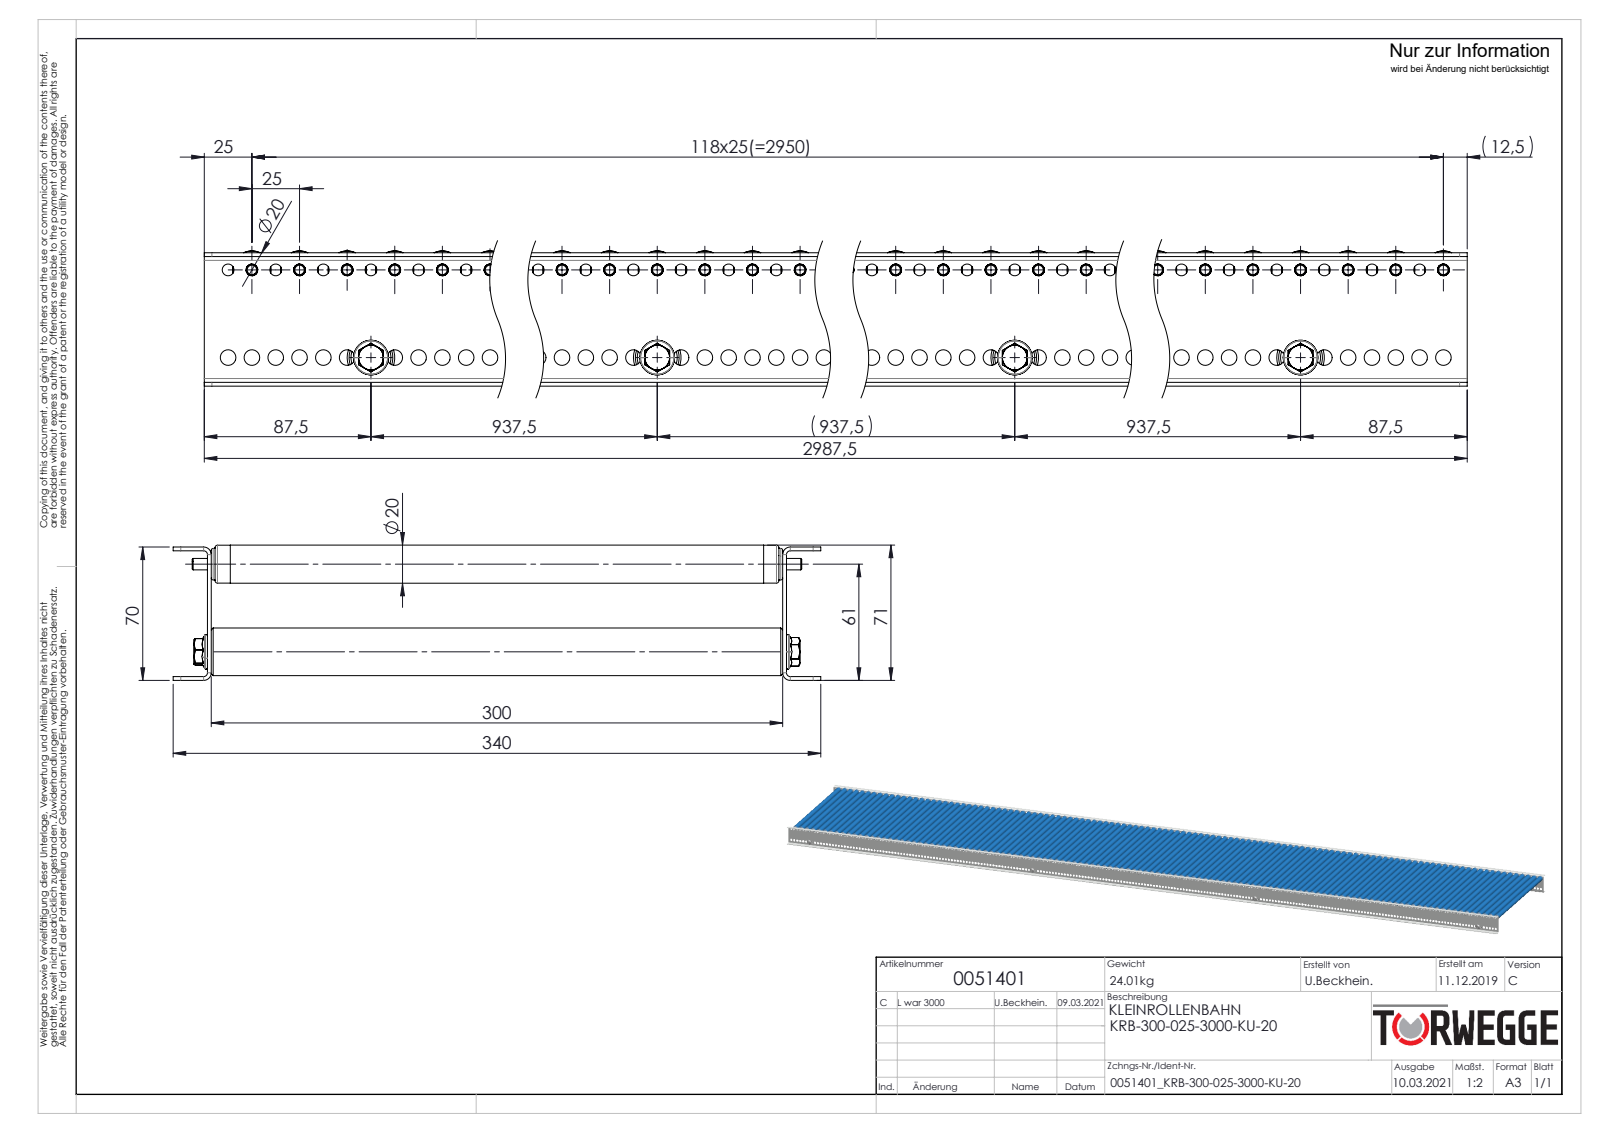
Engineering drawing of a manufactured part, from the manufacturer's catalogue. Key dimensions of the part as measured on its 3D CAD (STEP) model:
Part name (STEP PRODUCT): S100994_Sperrzahnschraube_M08x16-8.8-A2K; 0039777_Achse-Ø06-FA-KFG_L=320 fr D20; Profil_KRB-20x70x20x2_KFG_S109089_U-PROFIL-20-70-20-2-KRB-20-L=2987,5; KUT50-20x1,5-KU-A6_FA-EL=KFG_L=300 (+4 more)
STEP written by: SolidWorks 2020 (AUTOMOTIVE_DESIGN)
Units: millimetres
Bodies: 736 solids, 31448 faces (10438 planar, 11758 cylindrical, 9252 other)
Overall size (bounding box): 2987.5 × 340 × 71
Volume: 6 185 000 mm³ · Surface area: 7 059 000 mm²
Round holes (diameter × count): ⌀6.2 ×238, ⌀8.2 ×238, ⌀6.1 ×119, ⌀12.4 ×119, ⌀13.2 ×119, ⌀14.6 ×119, ⌀16.2 ×119, ⌀17 ×119, ⌀17.2 ×119, ⌀6.8 ×4, ⌀21 ×4
Round bosses / shafts (diameter × count): ⌀20 ×119, ⌀19.9 ×119, ⌀17.1 ×119, ⌀16.8 ×119, ⌀16.5 ×119, ⌀11.4 ×119, ⌀11.1 ×119, ⌀10.2 ×119
Partial cylindrical surfaces — rounded edges, fillets, slot ends (radius × count): R4.05 ×119, R4 ×8, R2 ×4
Main face-to-face distances: 2, 302, 68, 300, 304, 70, 66, 292, 10, 12
Hole centre spacings: 12.5, 25, 37.5, 50, 62.5, 75, 87.5, 100
